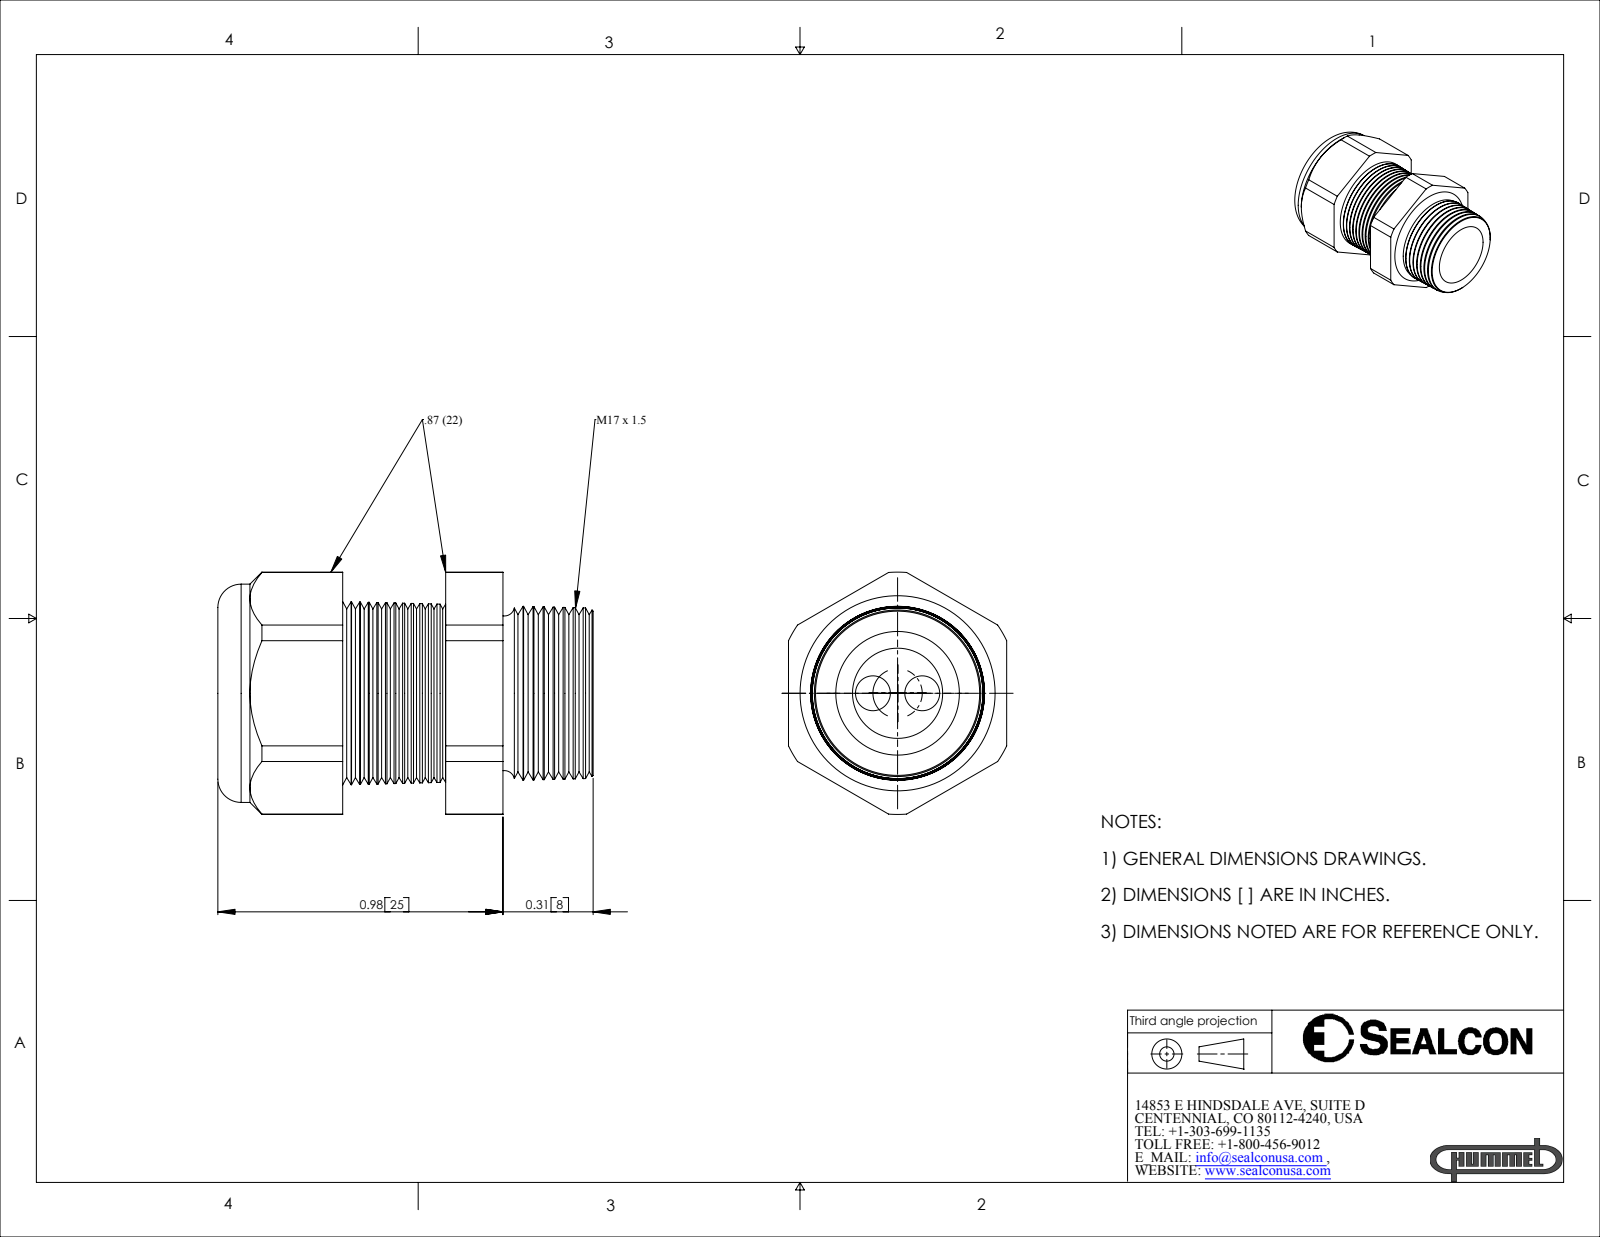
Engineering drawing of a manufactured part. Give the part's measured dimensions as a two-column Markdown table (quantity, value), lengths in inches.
| quantity | value |
| --- | --- |
| part name | CD17M1-GY |
| STEP written by | SolidWorks 2007 (CONFIG_CONTROL_DESIGN) |
| units | inches |
| bodies | 2 solids, 183 faces (21 planar, 24 cylindrical, 138 other) |
| overall size | 1.29 × 0.833 × 0.75 |
| volume | 0.354 in³ |
| surface area | 6.652 in² |
| round holes (diameter × count) | 0.12 × 2, 0.29 × 1, 0.31 × 1 |
| round bosses / shafts (diameter × count) | 0.75 × 1 |
| partial cylindrical surfaces (radius × count) | 0.416 × 1 |
| main face-to-face distances | 0.75, 0.75, 0.783, 0.429, 0.354, 0.98, 0.551, 0.197, 1.29, 0.861 |
| hole center spacings | 0.085, 0.169 |
